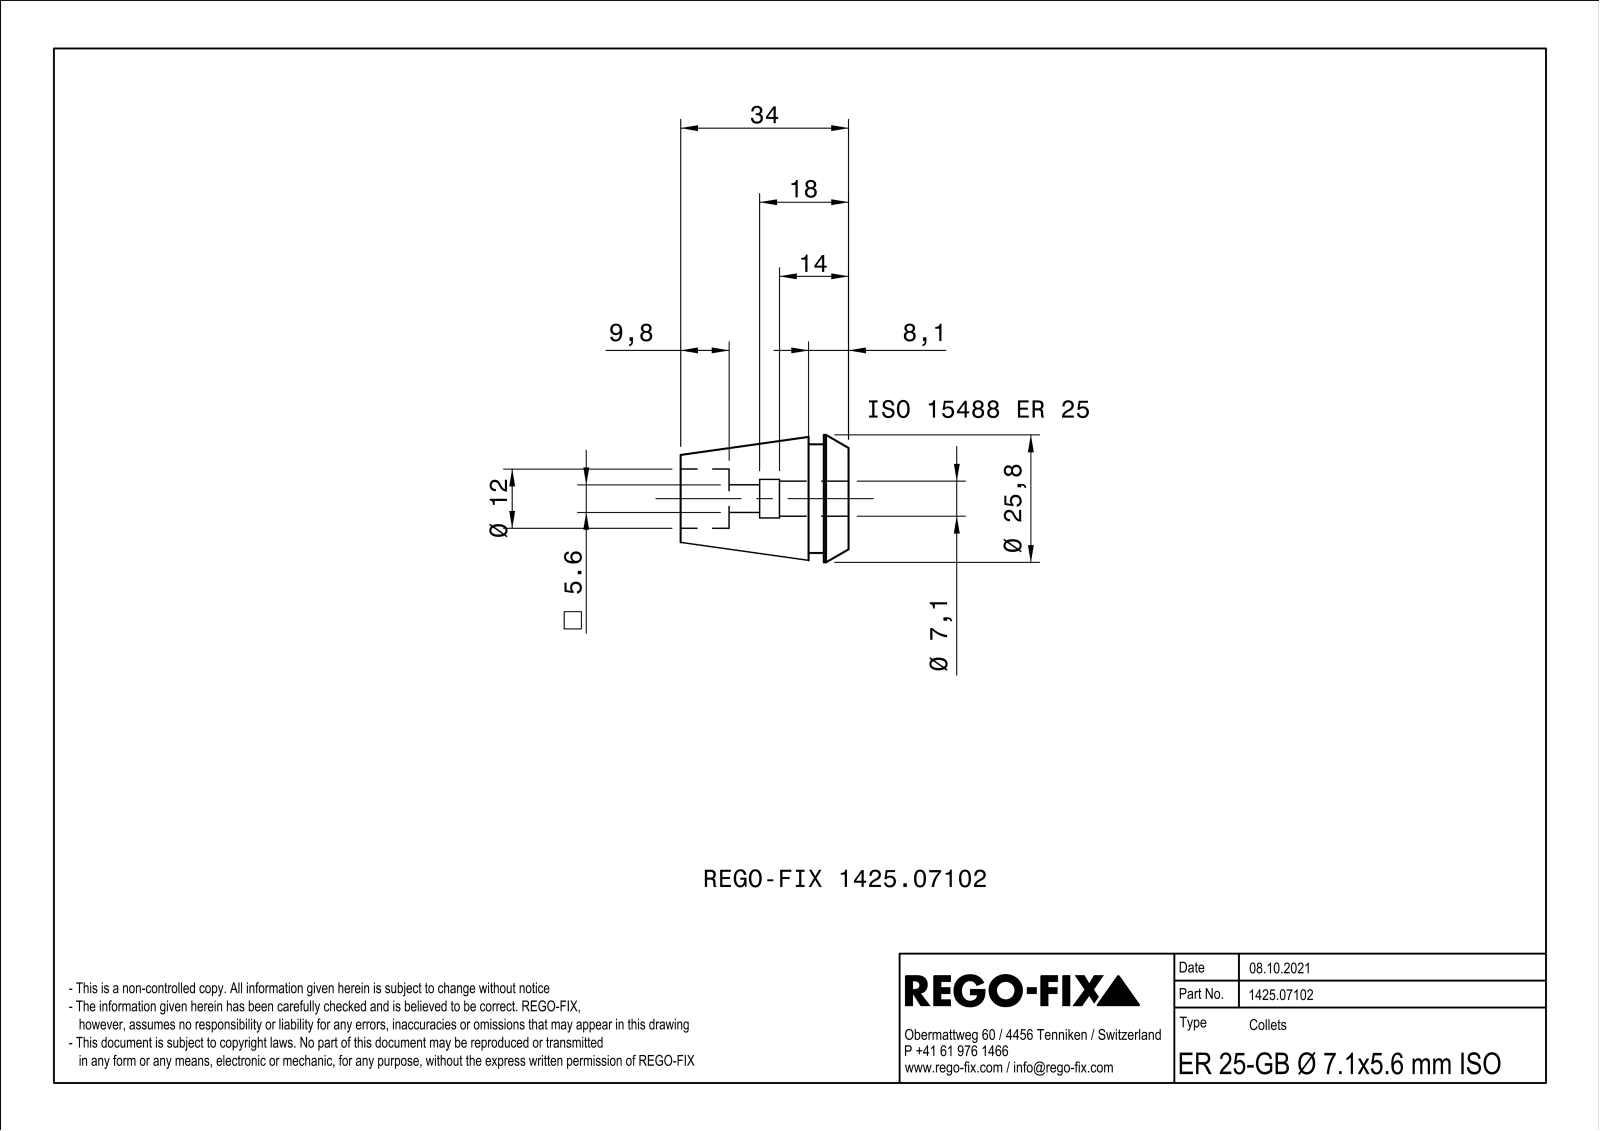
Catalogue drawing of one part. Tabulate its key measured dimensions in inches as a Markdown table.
| quantity | value |
| --- | --- |
| part name | NOCUT |
| STEP written by | SIEMENS PLM Software Solid Edge ST10 (AUTOMOTIVE_DESIGN) |
| units | inches |
| bodies | 1 solid, 160 faces (68 planar, 40 cylindrical, 52 other) |
| overall size | 1.339 × 1.015 × 1.015 |
| volume | 0.571 in³ |
| surface area | 10.52 in² |
| round holes (diameter × count) | 0.28 × 1, 0.472 × 1 |
| round bosses / shafts (diameter × count) | 1.016 × 1, 0.866 × 1 |
| partial cylindrical surfaces (radius × count) | 0.126 × 1, 0.148 × 1, 0.154 × 1 |
| main face-to-face distances | 0.031, 0.197, 1.339, 1.142, 0.319, 0.122, 1.02, 0.102, 0.134, 0.953 |
